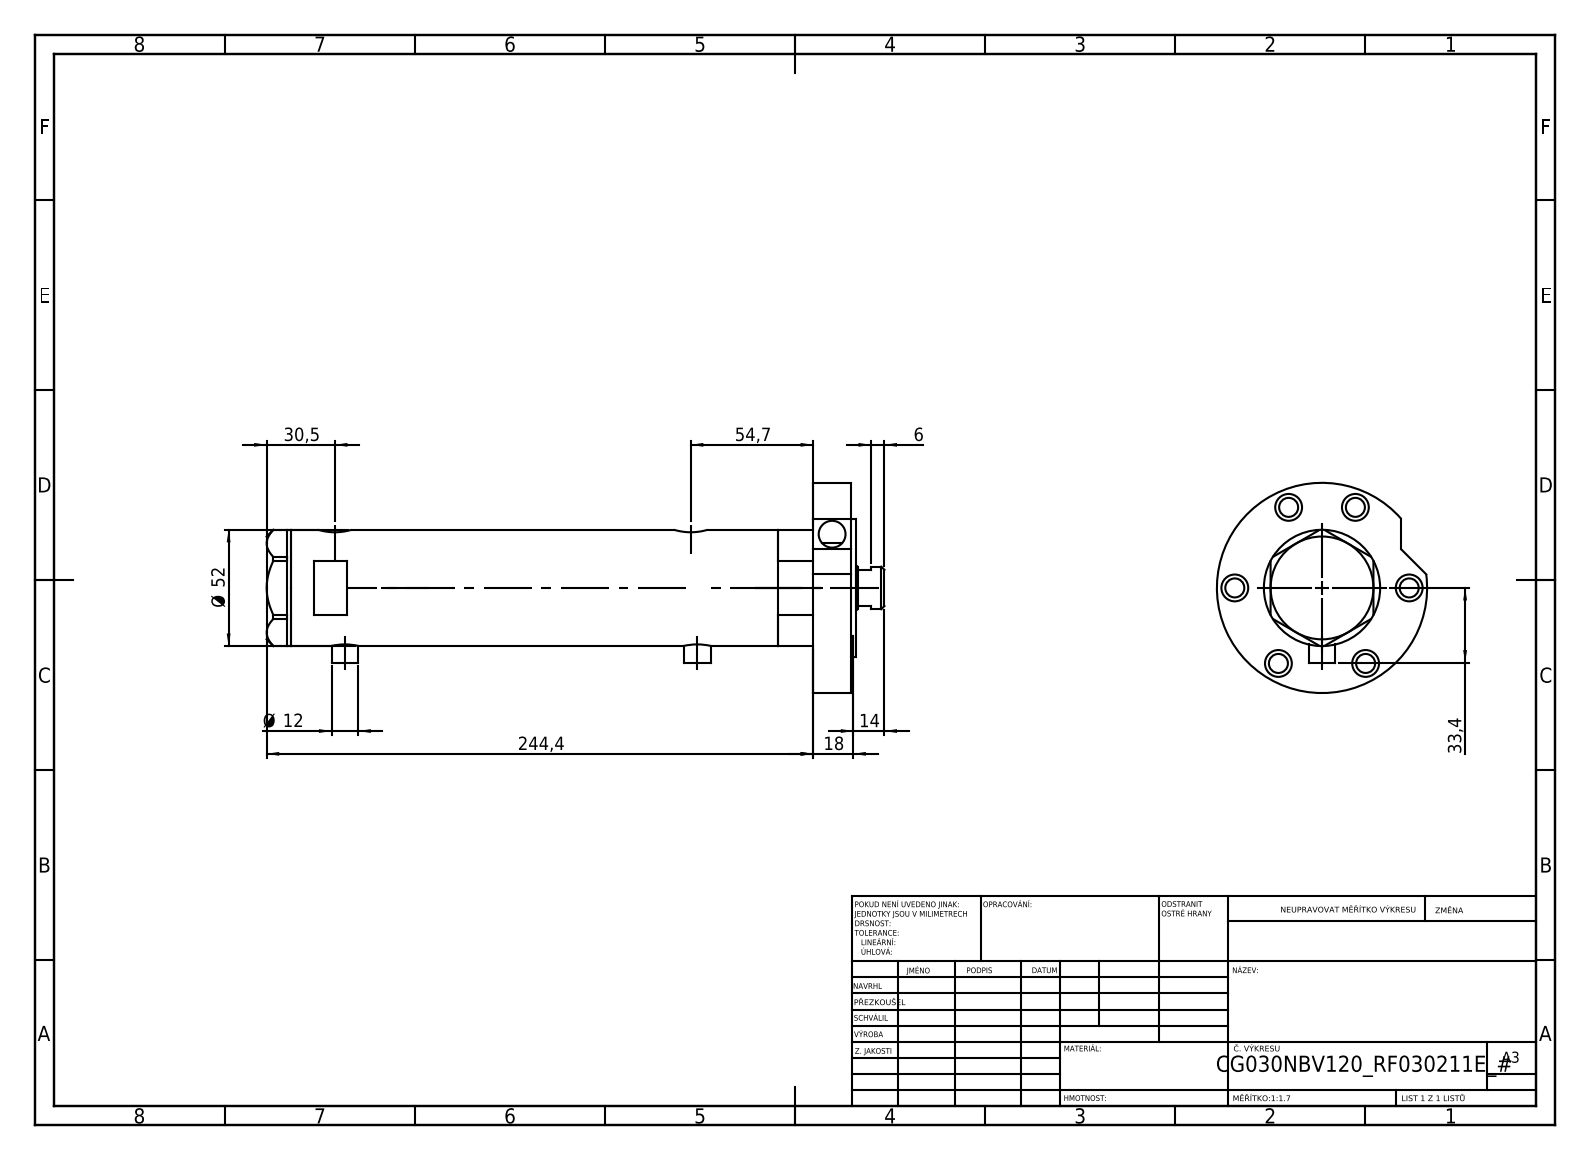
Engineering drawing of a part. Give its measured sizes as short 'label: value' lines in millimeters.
name: V270CG_FRONT; V270CG_VC; V270CG_RF211E; V270CG_MIDDLE (+1 more)
written by: SolidWorks 2019 (CONFIG_CONTROL_DESIGN)
unit: mm
bodies: 5 solids, 178 faces (76 planar, 82 cylindrical, 20 other)
size: 276.3 × 94 × 94
volume: 573 866 mm³; area: 129 935 mm²
holes: 7× ⌀12, 6× ⌀8.5, 2× ⌀9.73, 2× ⌀12.5, 2× ⌀15, 1× ⌀6.5, 1× ⌀20, 1× ⌀21.5, 1× ⌀30, 1× ⌀33, 1× ⌀40, 1× ⌀44
bosses: 2× ⌀12, 1× ⌀94, 1× ⌀62, 1× ⌀52, 1× ⌀38, 1× ⌀19
face distances: 17, 233.4, 250.4, 2, 252.4, 181.5, 51.9, 68.9, 70.9, 19
hole spacings: 39, 43.34, 64.85, 67.55, 69.95, 77.83, 2.9, 4.5
